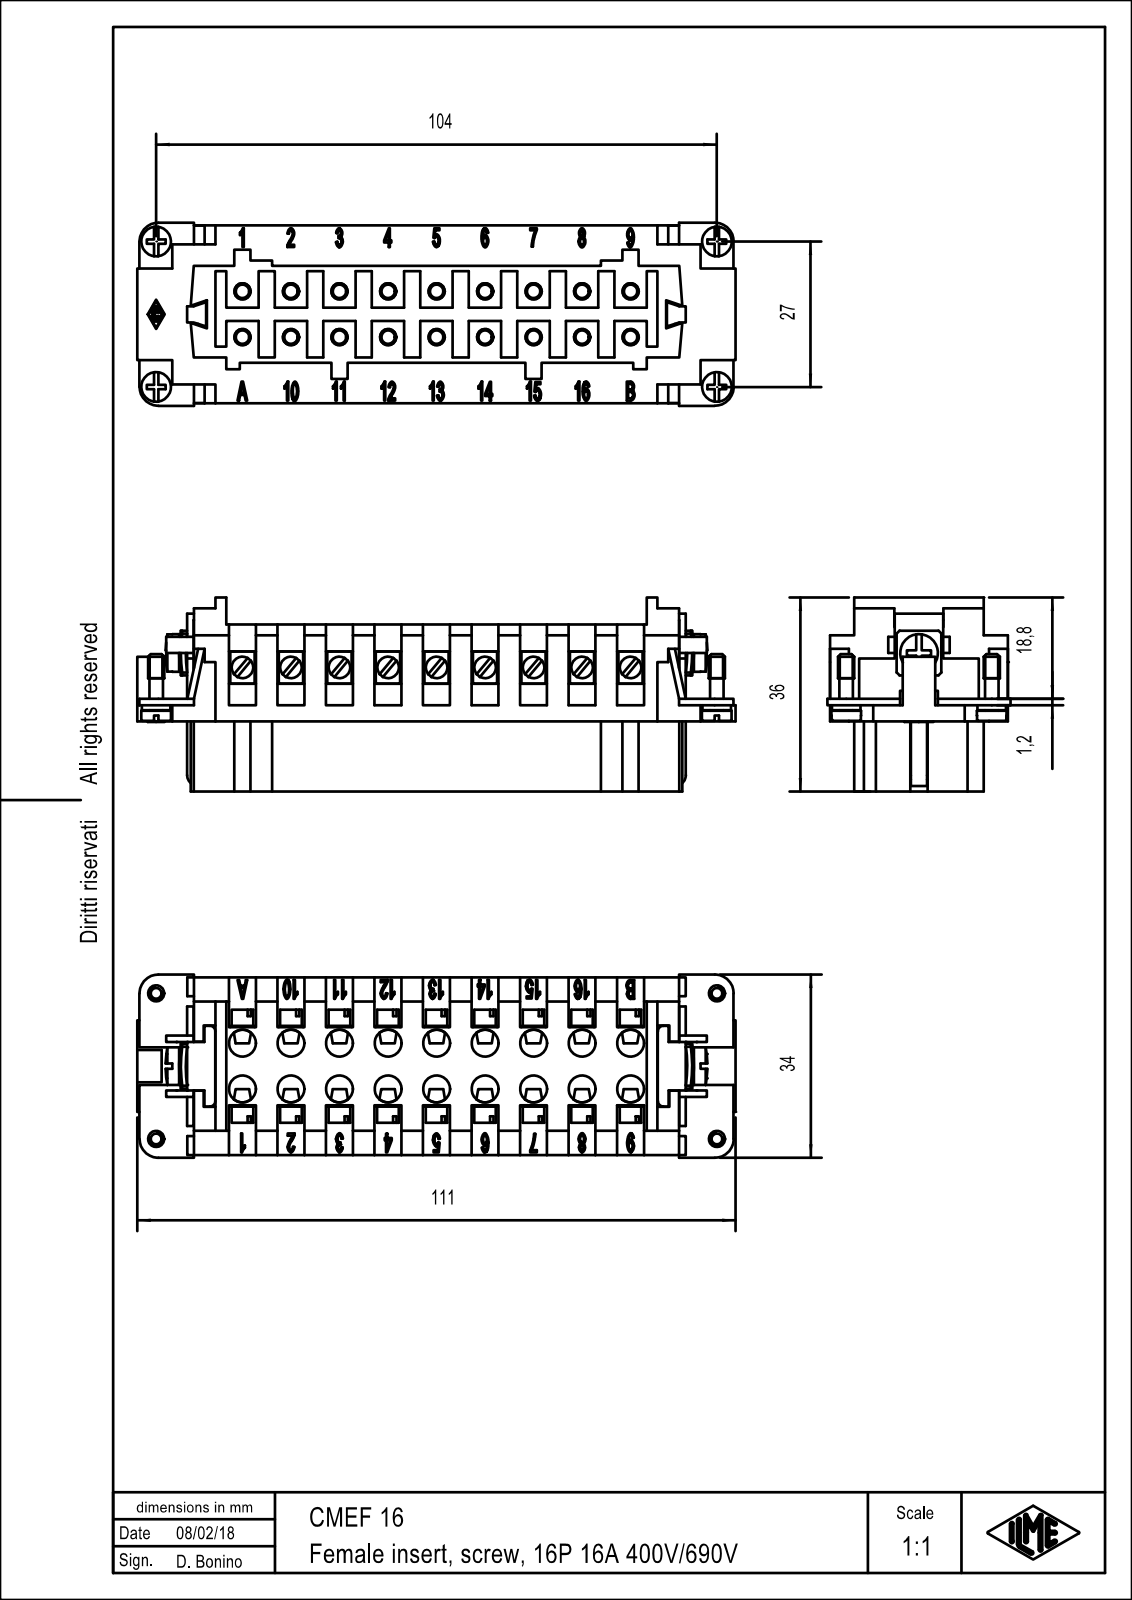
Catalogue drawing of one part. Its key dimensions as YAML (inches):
part_name: "CMEF 16"
step_written_by: "Autodesk Inventor 7 (AUTOMOTIVE_DESIGN)"
units: inches
bodies: {solids: 1, faces: 2055, planar: 1029, cylindrical: 214, other: 812}
overall_size: [4.37, 1.417, 1.339]
volume: 3.312
surface_area: 65.48
round_holes:
  - {diameter: 0.118, count: 18}
  - {diameter: 0.197, count: 18}
  - {diameter: 0.098, count: 9}
  - {diameter: 0.1, count: 2}
round_bosses_or_shafts:
  - {diameter: 0.157, count: 9}
  - {diameter: 0.217, count: 2}
  - {diameter: 0.209, count: 2}
  - {diameter: 0.118, count: 2}
  - {diameter: 0.098, count: 2}
  - {diameter: 0.276, count: 1}
partial_cylinders:
  - {radius: 0.098, count: 18}
  - {radius: 0.004, count: 14}
  - {radius: 0.039, count: 2}
  - {radius: 0.079, count: 2}
  - {radius: 0.138, count: 2}
  - {radius: 0.217, count: 1}
face_to_face_distances: [0.709, 0.236, 0.118, 0.354, 0.591, 0.079, 0.512, 1.299, 0.6, 0.157]
hole_center_spacings: [0.354, 0.487, 0.709, 0.784, 1.063, 1.115, 1.417, 1.456]
